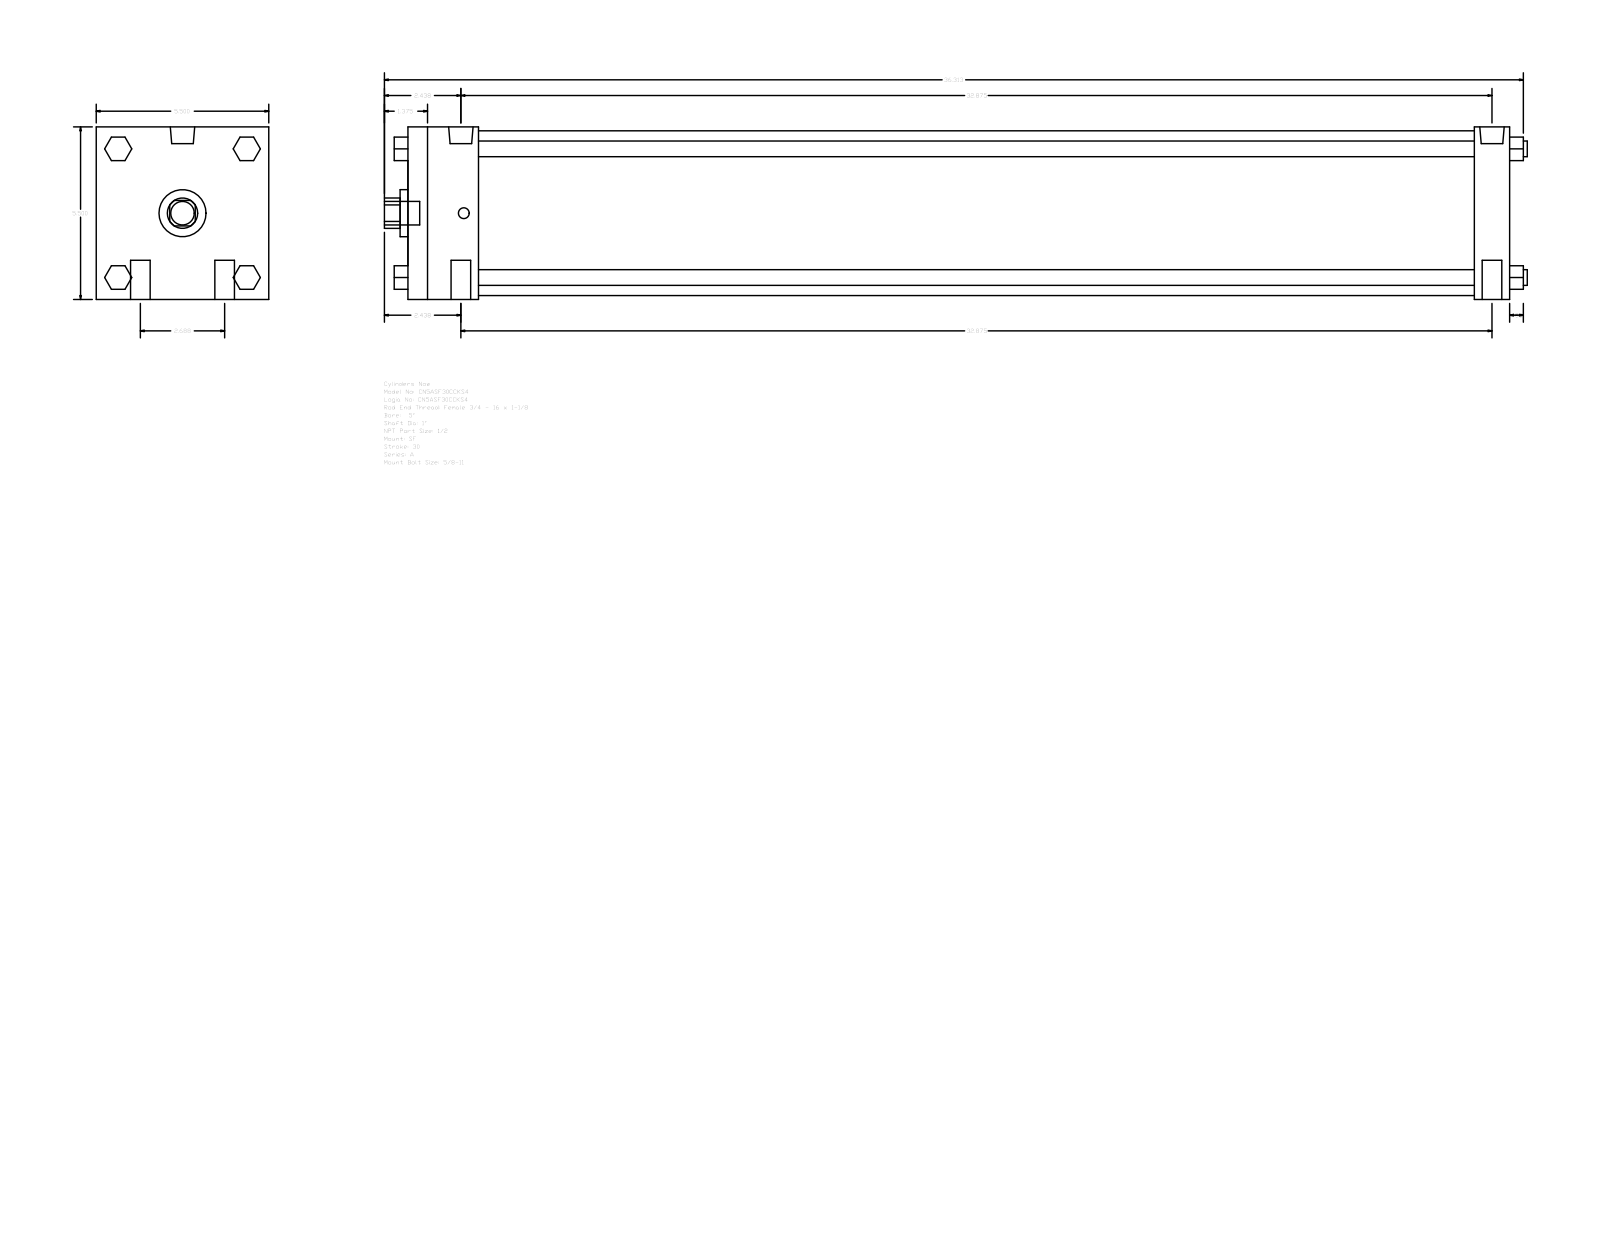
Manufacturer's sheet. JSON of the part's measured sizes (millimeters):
{"part_name": "A_SF__0500_1", "step_written_by": "GSSL Pune (CONFIG_CONTROL_DESIGN)", "units": "millimeters", "bodies": {"solids": 0, "faces": 124, "planar": 94, "cylindrical": 30, "other": 0}, "overall_size": [925.51, 139.7, 139.7], "round_holes": [[25.4, 1], [38.1, 1], [133.35, 1]], "round_bosses_or_shafts": [[15.88, 4], [12.7, 4], [19.77, 2], [8.73, 2], [19.05, 1]], "partial_cylinders_radius": [[12.29, 1]], "face_to_face_distances": [139.7, 892.18, 57.15, 863.6, 806.45, 835.03, 28.58, 19.05, 52.07, 90.18]}
